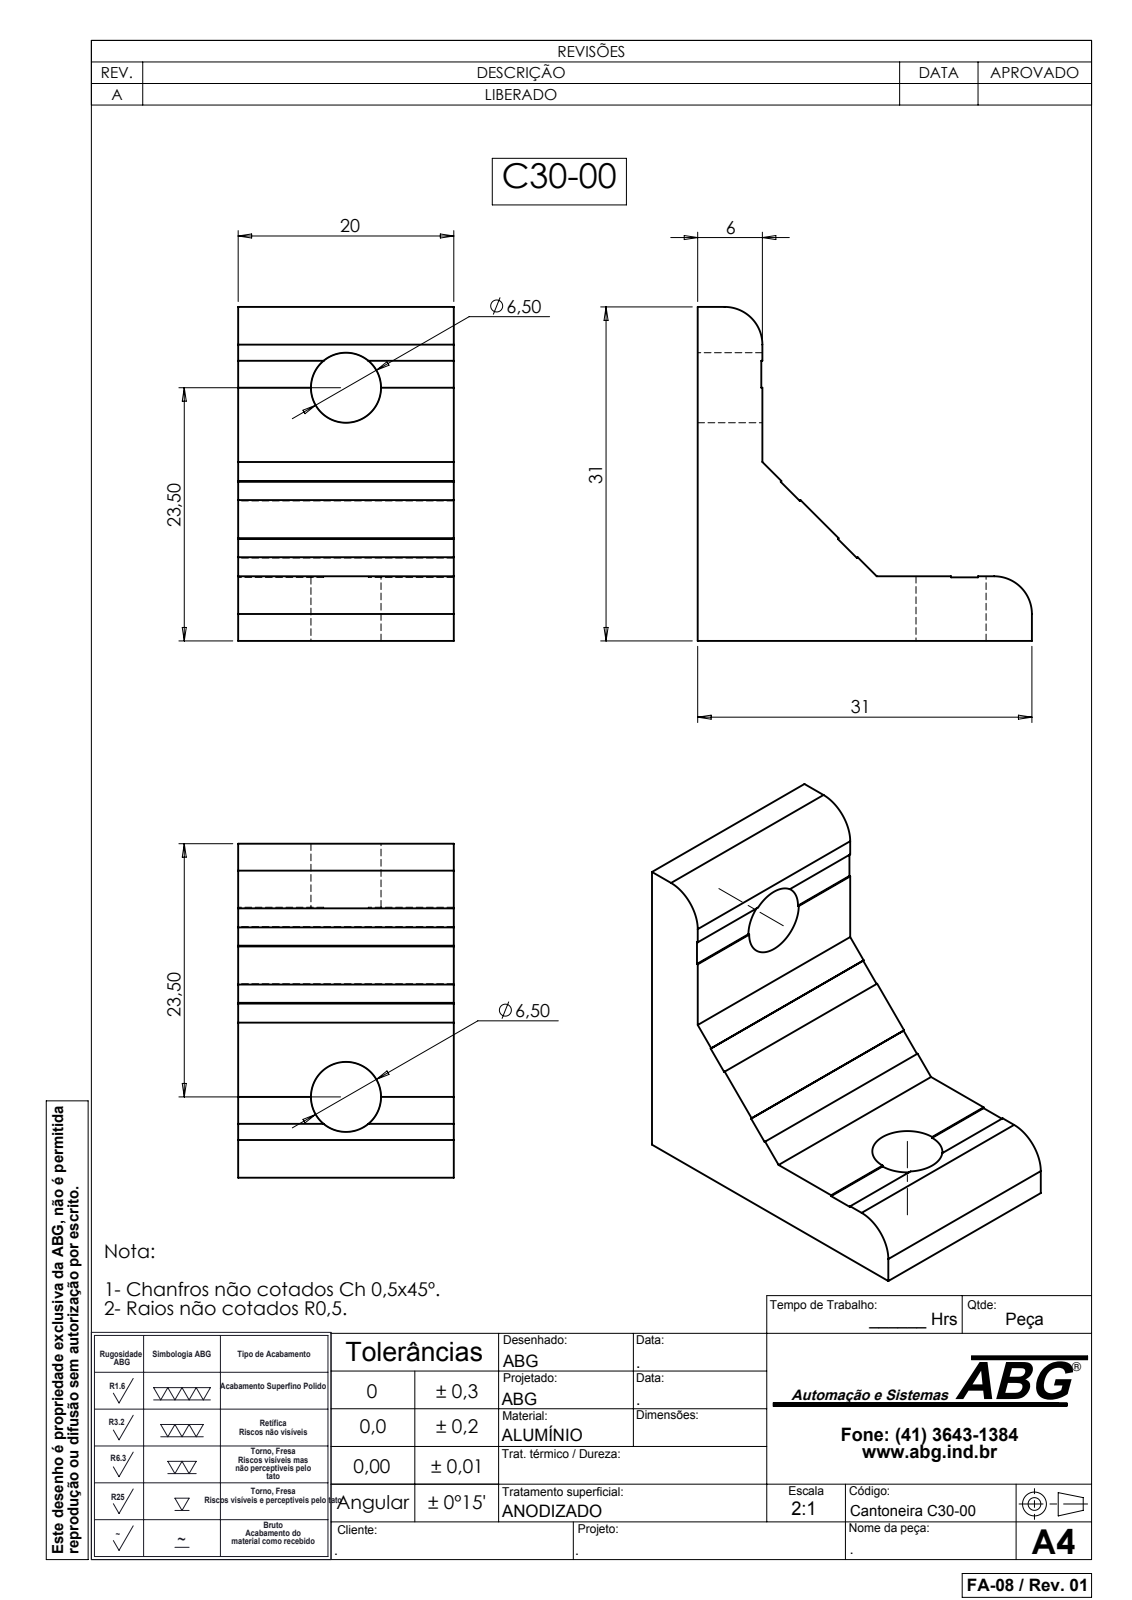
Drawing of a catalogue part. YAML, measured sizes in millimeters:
part_name: "C30-00"
step_written_by: "SolidWorks 2007 (CONFIG_CONTROL_DESIGN)"
units: millimeters
bodies: {solids: 1, faces: 37, planar: 31, cylindrical: 6, other: 0}
overall_size: [31, 31, 20]
volume: 7325
surface_area: 3193
round_holes:
  - {diameter: 6.5, count: 2}
partial_cylinders:
  - {radius: 3.5, count: 2}
face_to_face_distances: [20, 6, 25, 31, 25.1, 5.9, 7.5, 2.5, 5, 20.1]
